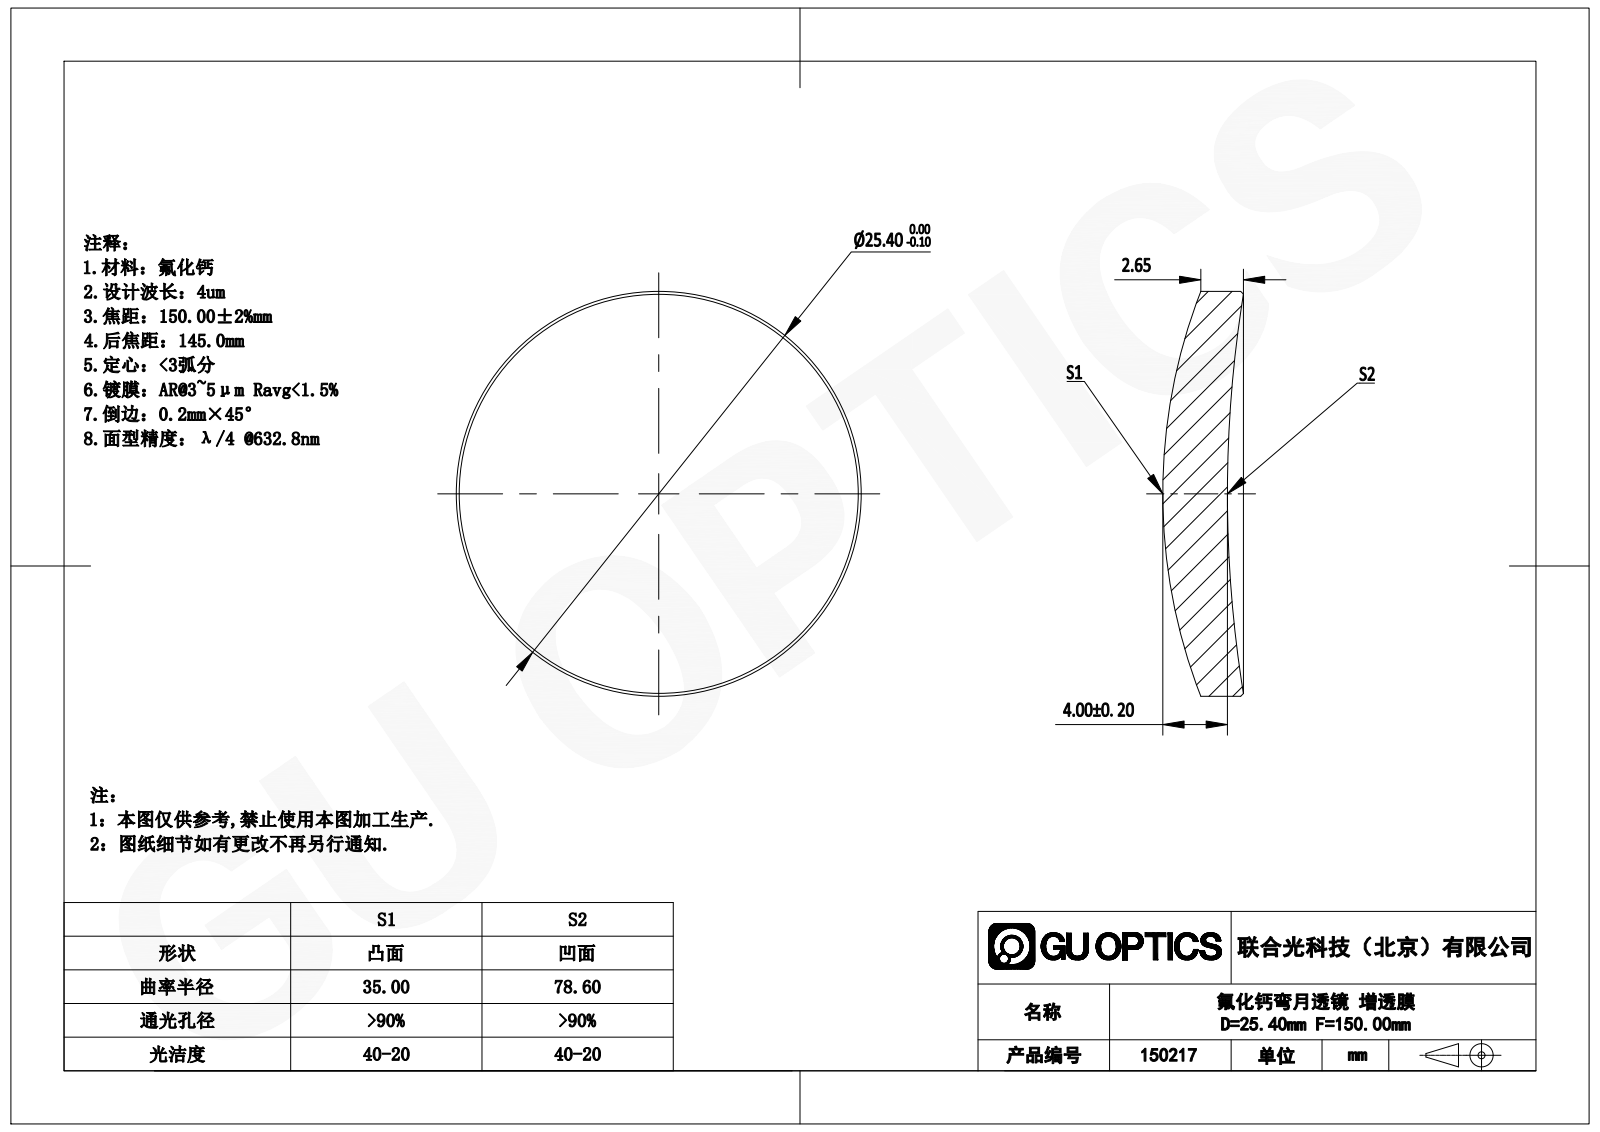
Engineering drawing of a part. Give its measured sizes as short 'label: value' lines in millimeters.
name: GLM5-025B-150-IR1
written by: SolidWorks 2022 (AUTOMOTIVE_DESIGN)
unit: mm
bodies: 1 solid, 8 faces (0 planar, 2 cylindrical, 6 other)
size: 25.4 × 25.4 × 5.06
volume: 1 716 mm³; area: 1 240 mm²
bosses: 1× ⌀25.4
